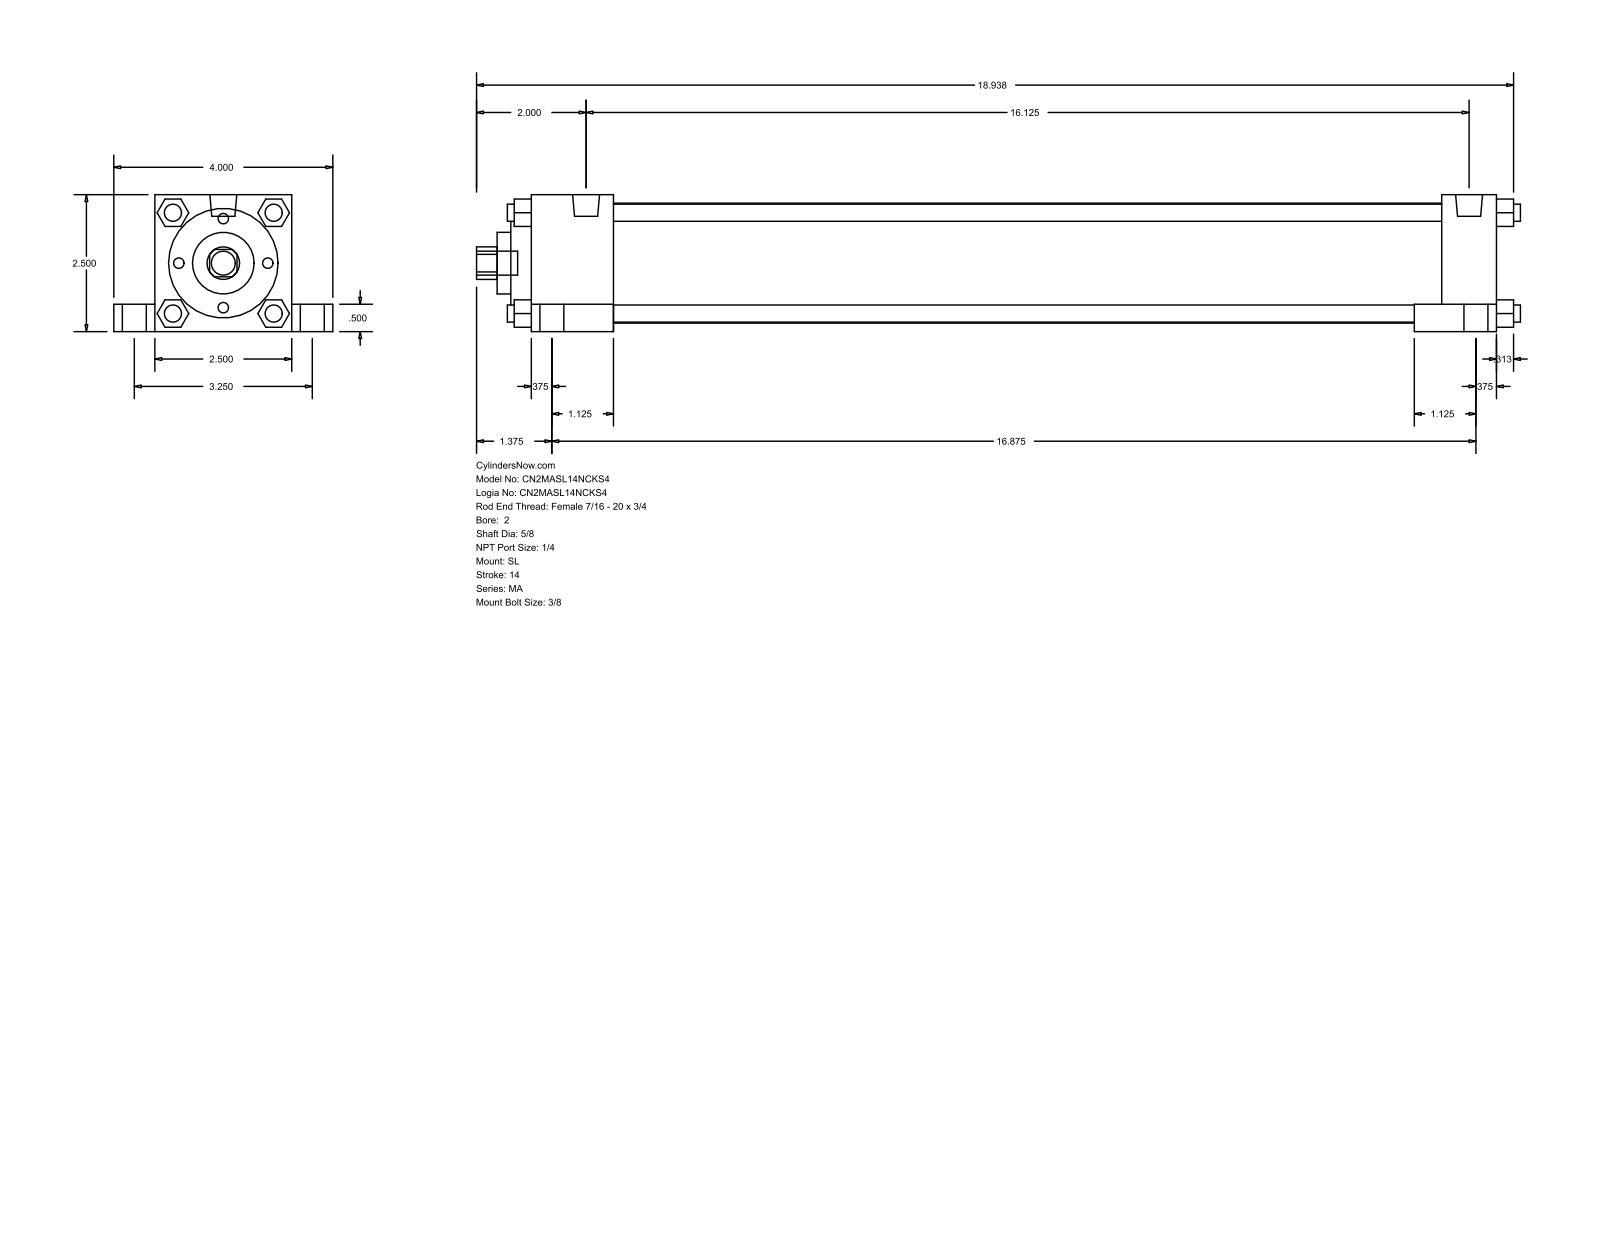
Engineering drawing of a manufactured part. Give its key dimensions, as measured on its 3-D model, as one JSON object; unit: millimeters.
{"part_name": "MA_SL__0200_0.625", "step_written_by": "GSSL Pune (CONFIG_CONTROL_DESIGN)", "units": "millimeters", "bodies": {"solids": 0, "faces": 150, "planar": 113, "cylindrical": 37, "other": 0}, "overall_size": [484.19, 101.6, 63.5], "round_holes": [[15.88, 1], [28.57, 1], [50.8, 1], [55.63, 1]], "round_bosses_or_shafts": [[7.94, 8], [11.11, 5], [17.46, 4], [12.49, 2]], "partial_cylinders_radius": [[7.54, 1]], "face_to_face_distances": [63.5, 12.7, 9.52, 19.05, 82.55, 38.1, 50.8, 447.67, 409.57, 422.28]}
